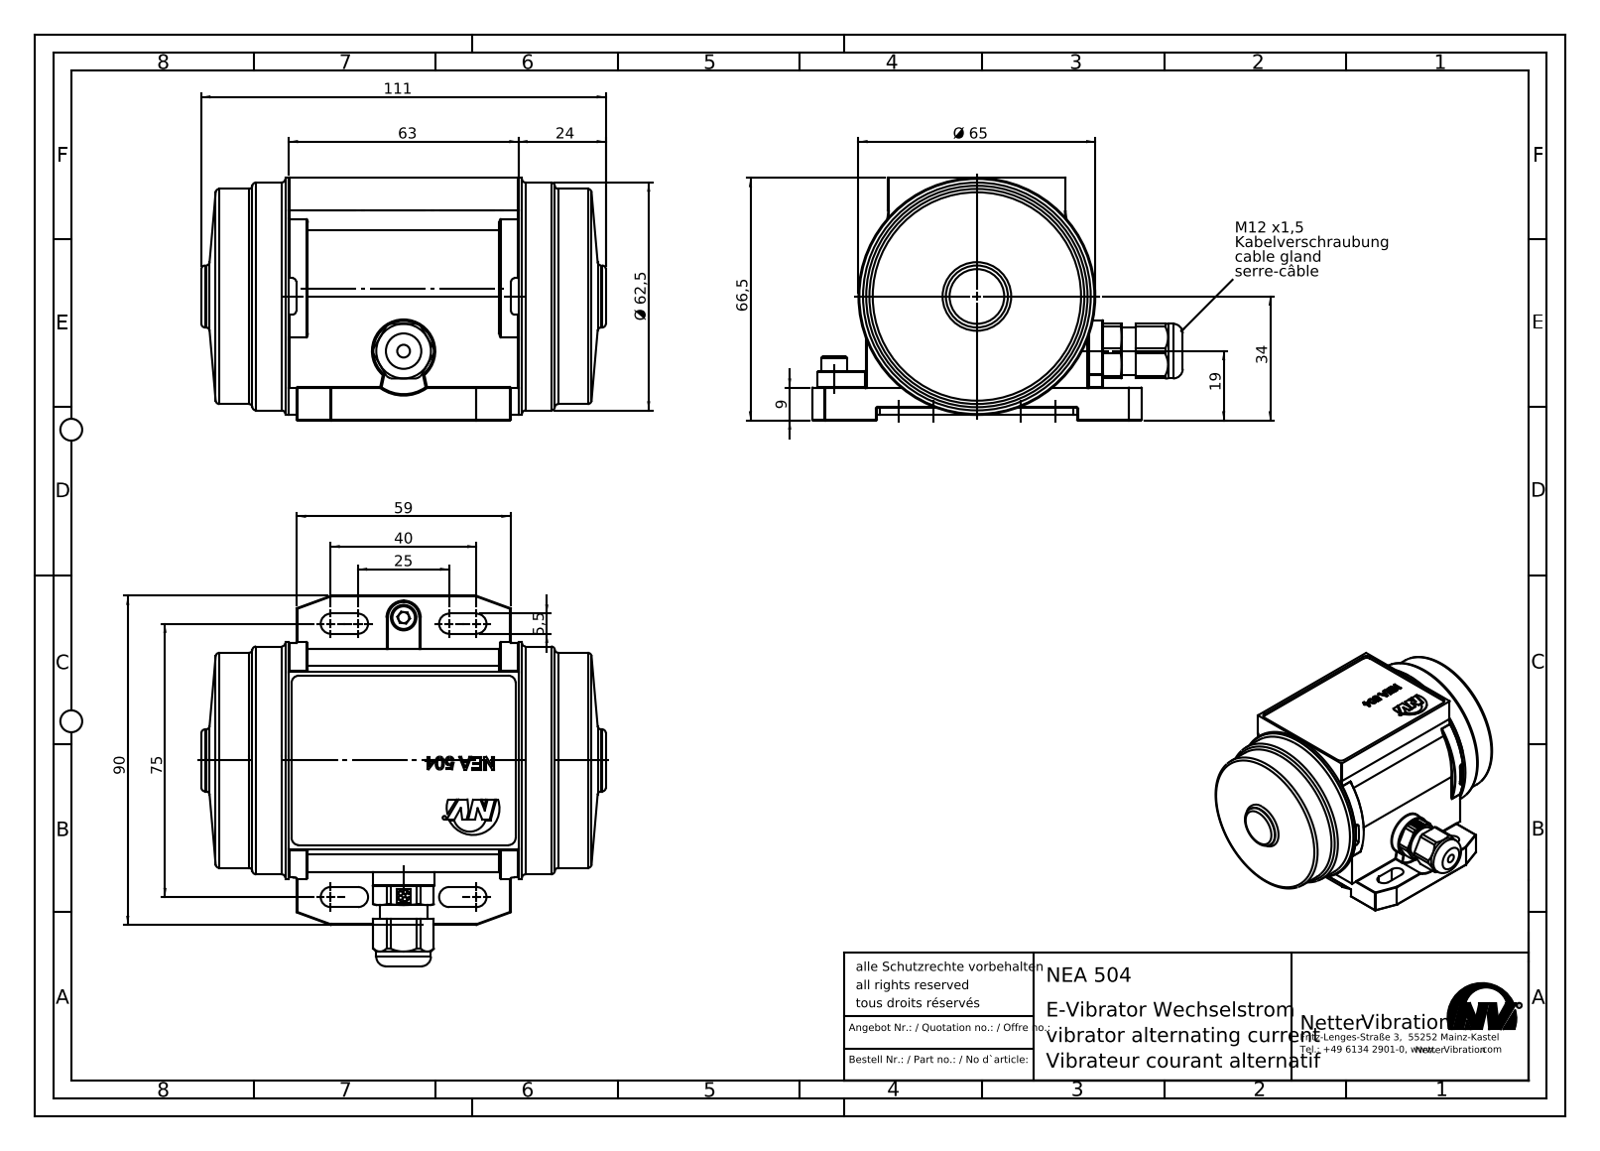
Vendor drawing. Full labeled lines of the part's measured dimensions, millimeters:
Part name (STEP PRODUCT): NEA 504
STEP written by: SolidWorks 2015 (AUTOMOTIVE_DESIGN)
Units: millimetres
Bodies: 9 solids, 814 faces (296 planar, 262 cylindrical, 256 other)
Overall size (bounding box): 111 × 101.65 × 66.5
Volume: 298 298 mm³ · Surface area: 69 362 mm²
Round holes (diameter × count): ⌀1.16 ×5, ⌀4.2 ×5, ⌀3.5 ×1, ⌀10.5 ×1, ⌀14 ×1, ⌀15 ×1, ⌀54.5 ×1, ⌀57 ×1, ⌀60.5 ×1
Round bosses / shafts (diameter × count): ⌀4 ×5, ⌀7.64 ×4, ⌀65 ×1, ⌀62.5 ×1, ⌀61 ×1, ⌀59 ×1, ⌀58 ×1, ⌀17 ×1
Partial cylindrical surfaces — rounded edges, fillets, slot ends (radius × count): R0.2 ×73, R2.75 ×8, R1 ×4, R2 ×4, R5 ×4, R4.49 ×2, R10 ×2, R21.48 ×2
Main face-to-face distances: 64, 79, 1.5, 8, 71, 69.5, 65.5, 61, 9, 5.5
Hole centre spacings: 1.22, 1.98, 43, 46.6, 63.41, 64.98, 27, 27.18
